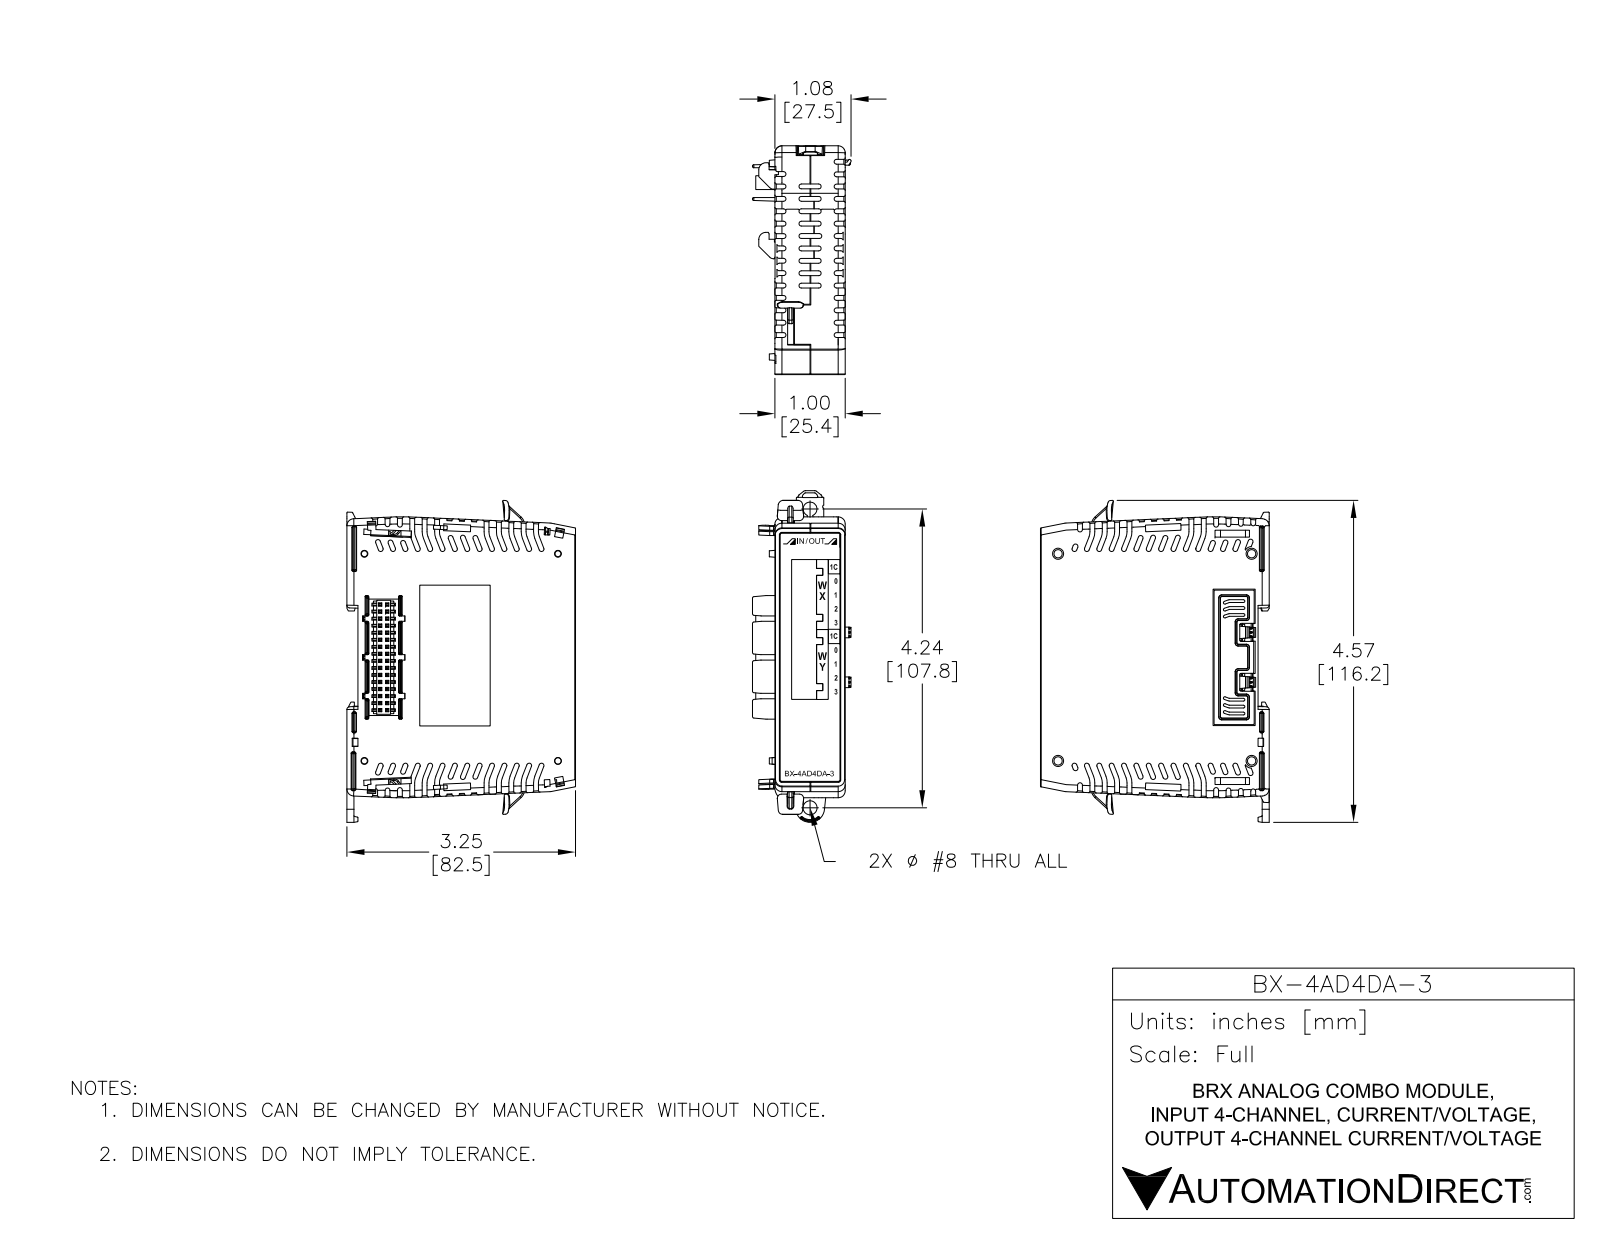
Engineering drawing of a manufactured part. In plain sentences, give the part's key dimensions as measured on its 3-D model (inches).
The part is named "BX-4AD4DA-3". Its 3-D file was written by "SolidWorks 2017 (AUTOMOTIVE_DESIGN)". It is 5 solids with 3757 faces: 2670 planar, 603 cylindrical and 484 other. Overall it measures 4.586 by 3.25 by 1.402 inches. Its volume is 11.58 cubic inches and its surface area 72.37 square inches. Round holes: 2 of diameter 0.047, 2 of diameter 0.065, 2 of diameter 0.118, 2 of diameter 0.118, 1 of diameter 0.199. Round bosses or shafts: 2 of diameter 0.062, 2 of diameter 0.059. Partial cylindrical surfaces (rounded edges, fillets, slot ends): 102 of radius 0.005, 61 of radius 0.008, 47 of radius 0.01, 34 of radius 0.02, 24 of radius 0.005, 14 of radius 0.117, 13 of radius 0.039, 12 of radius 0.01. The main face-to-face distances are 1, 3.211, 3.22, 0.475, 0.157, 3.053, 3.063, 0.1, 0.039, 0.787. The hole center spacings are 0.1, 0.824, 0.919, 1.3, 2.093, 2.193, 2.585, 2.617.
